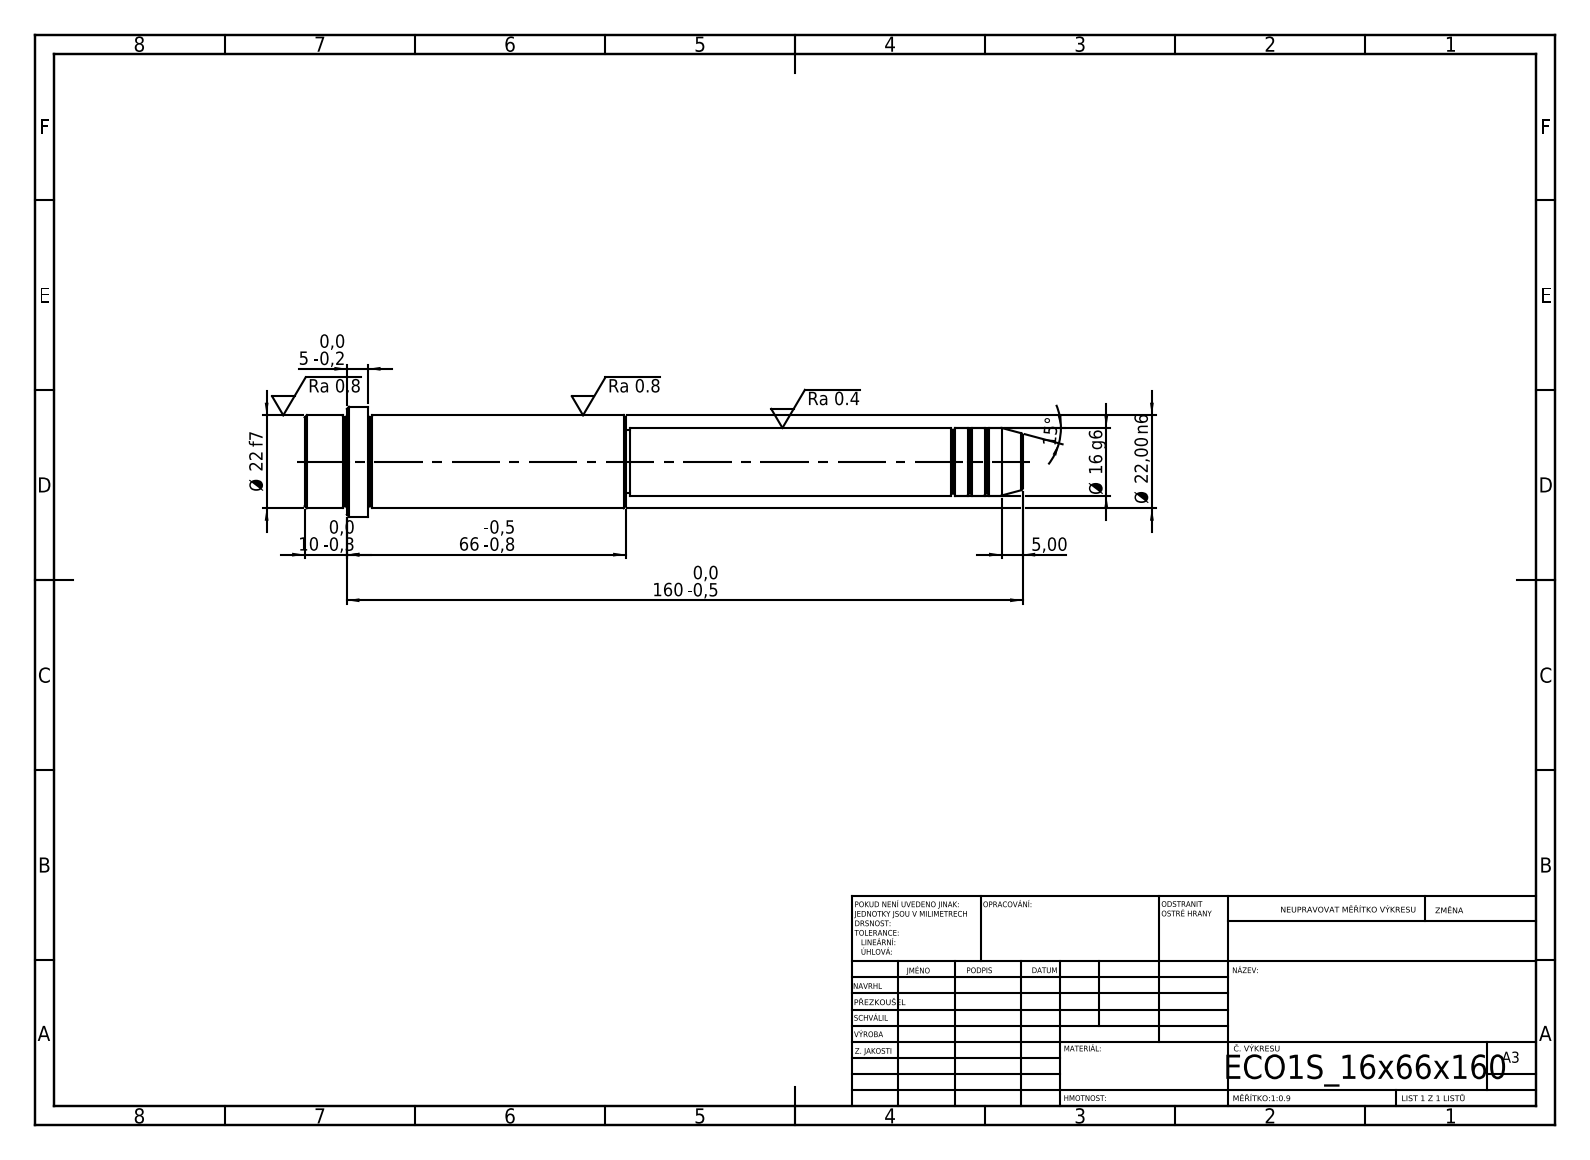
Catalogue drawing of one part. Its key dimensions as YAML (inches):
step_written_by: "SolidWorks 2019 (CONFIG_CONTROL_DESIGN)"
units: inches
bodies: {solids: 1, faces: 52, planar: 6, cylindrical: 16, other: 30}
overall_size: [6.693, 1.024, 1.024]
volume: 2.943
surface_area: 17.29
round_bosses_or_shafts:
  - {diameter: 1.024, count: 1}
  - {diameter: 0.866, count: 1}
  - {diameter: 0.63, count: 1}
  - {diameter: 0.591, count: 1}
face_to_face_distances: [2.992, 2.402, 0.591, 3.701, 6.102, 6.693, 6.299, 2.598, 0.197, 0.394]
